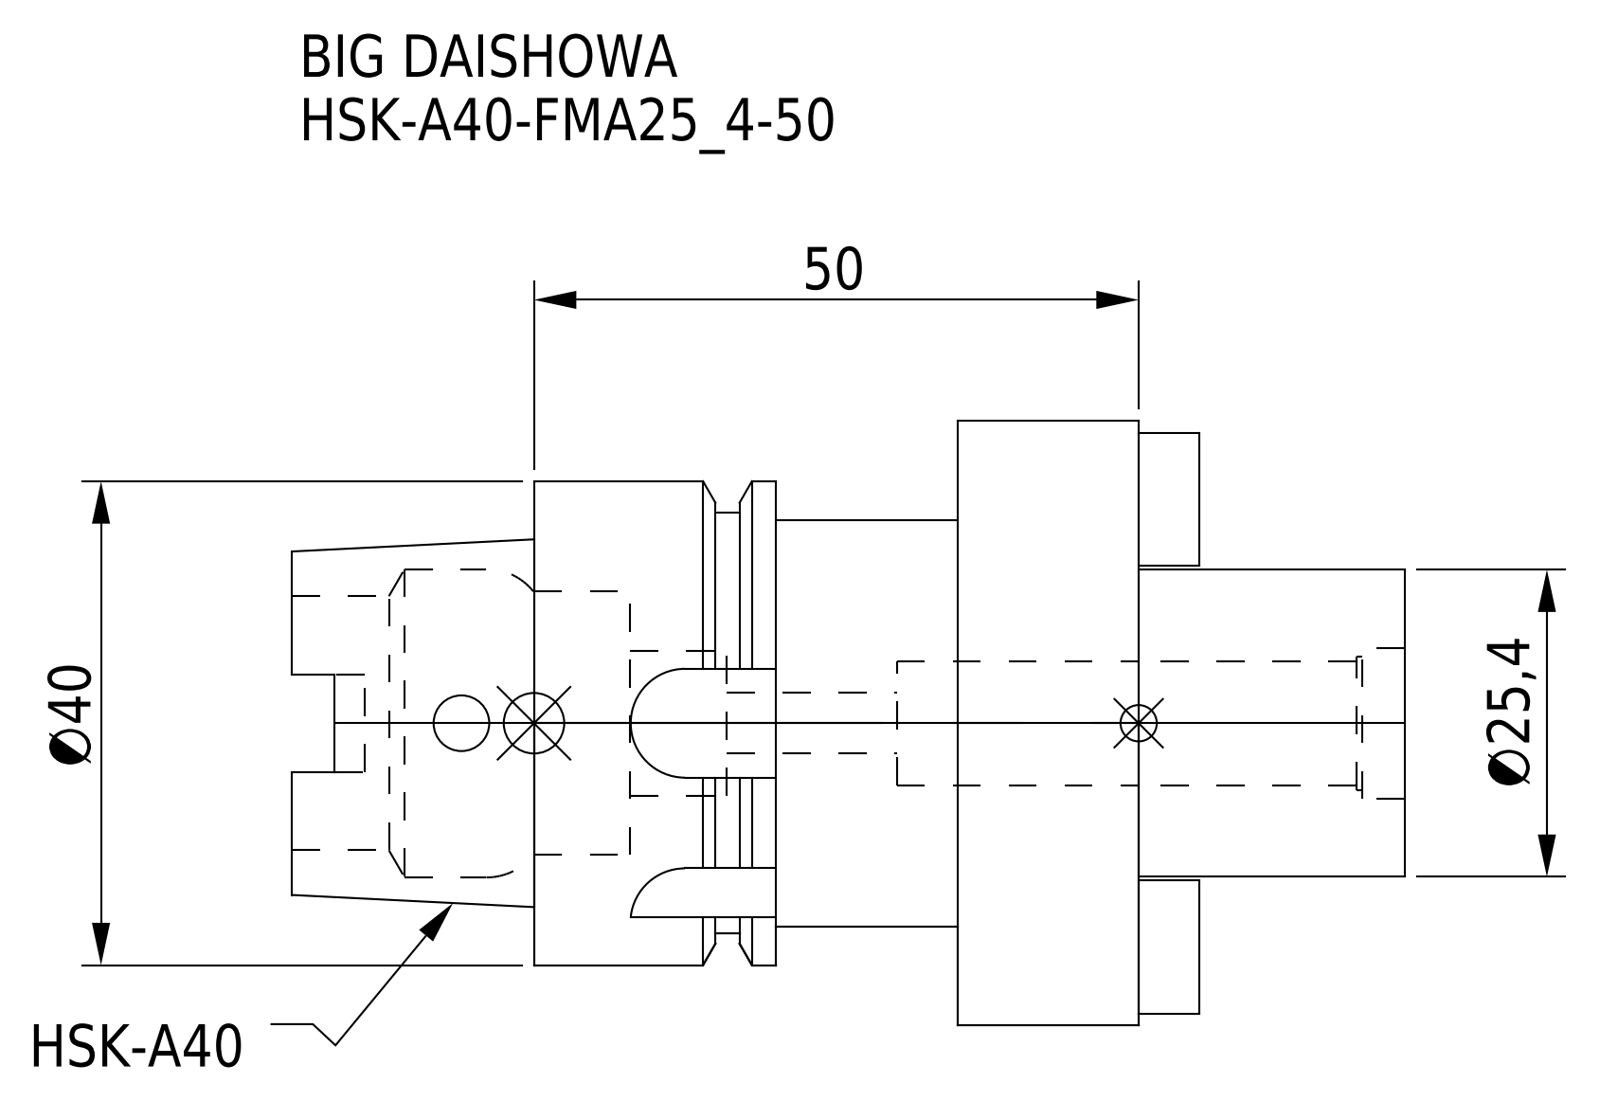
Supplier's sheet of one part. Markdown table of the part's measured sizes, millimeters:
| quantity | value |
| --- | --- |
| part name | HSK-A40-FMA25_4-50 |
| STEP written by | CREO PARAMETRIC BY PTC INC, 2016380 (AUTOMOTIVE_DESIGN) |
| units | millimeters |
| bodies | 1 solid, 111 faces (51 planar, 46 cylindrical, 14 other) |
| overall size | 92 × 50 × 50 |
| volume | 75 493 mm³ |
| surface area | 19 330 mm² |
| round holes (diameter × count) | 4.6 × 1, 5 × 1, 10.25 × 1, 11 × 1, 12 × 1, 12.5 × 1, 21 × 1, 21.8 × 1, 25.5 × 1 |
| round bosses / shafts (diameter × count) | 50 × 1, 40 × 1, 34.8 × 1, 33.6 × 1, 25.4 × 1 |
| partial cylindrical surfaces (radius × count) | 1.88 × 4, 4.5 × 4 |
| main face-to-face distances | 15, 35, 20, 50, 37, 55, 22, 72, 5, 30 |
